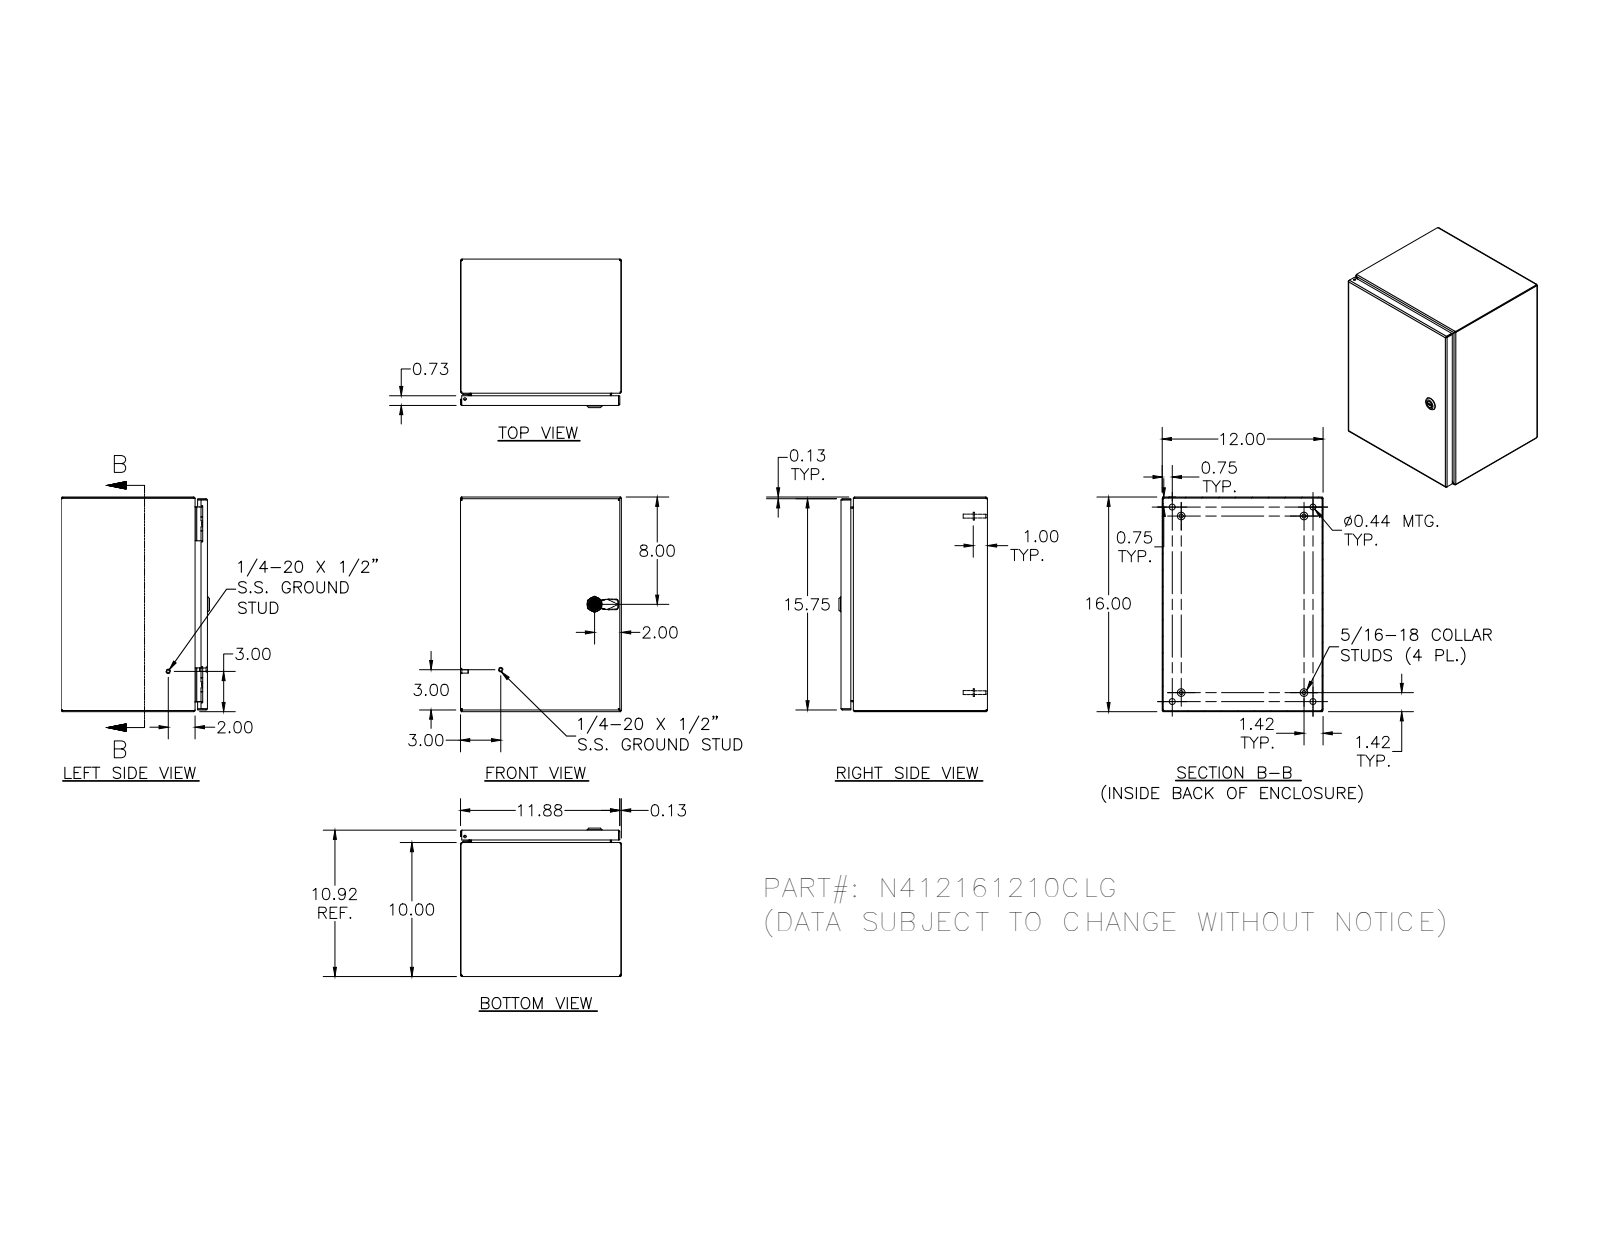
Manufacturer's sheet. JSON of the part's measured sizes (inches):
{"part_name": "N412161210CLG", "step_written_by": "SolidWorks 2018 (AUTOMOTIVE_DESIGN)", "units": "inches", "bodies": {"solids": 33, "faces": 1449, "planar": 530, "cylindrical": 547, "other": 372}, "overall_size": [16, 12, 11.075], "volume_in3": 78.69, "surface_area_in2": 2144, "round_holes": [[0.188, 5], [0.093, 4], [0.152, 4], [0.167, 4], [0.172, 4], [0.437, 4], [0.156, 2], [0.187, 1], [0.197, 1], [0.315, 1], [0.394, 1], [0.402, 1]], "round_bosses_or_shafts": [[0.25, 10], [0.563, 4], [0.36, 4], [0.32, 4], [0.3, 4], [0.275, 4], [0.256, 4], [0.164, 4]], "partial_cylinders_radius": [[0.012, 30], [0.031, 30], [0.05, 26], [0.105, 20], [0.016, 18], [0.125, 16], [0.02, 13], [0.032, 8]], "face_to_face_distances": [0.074, 10.843, 0.074, 10.769, 10.917, 11.926, 12, 11.852, 11.926, 15.852], "hole_center_spacings": [12, 0.66, 0.656, 1.307, 1.965, 0.5, 0.984, 1.311]}
